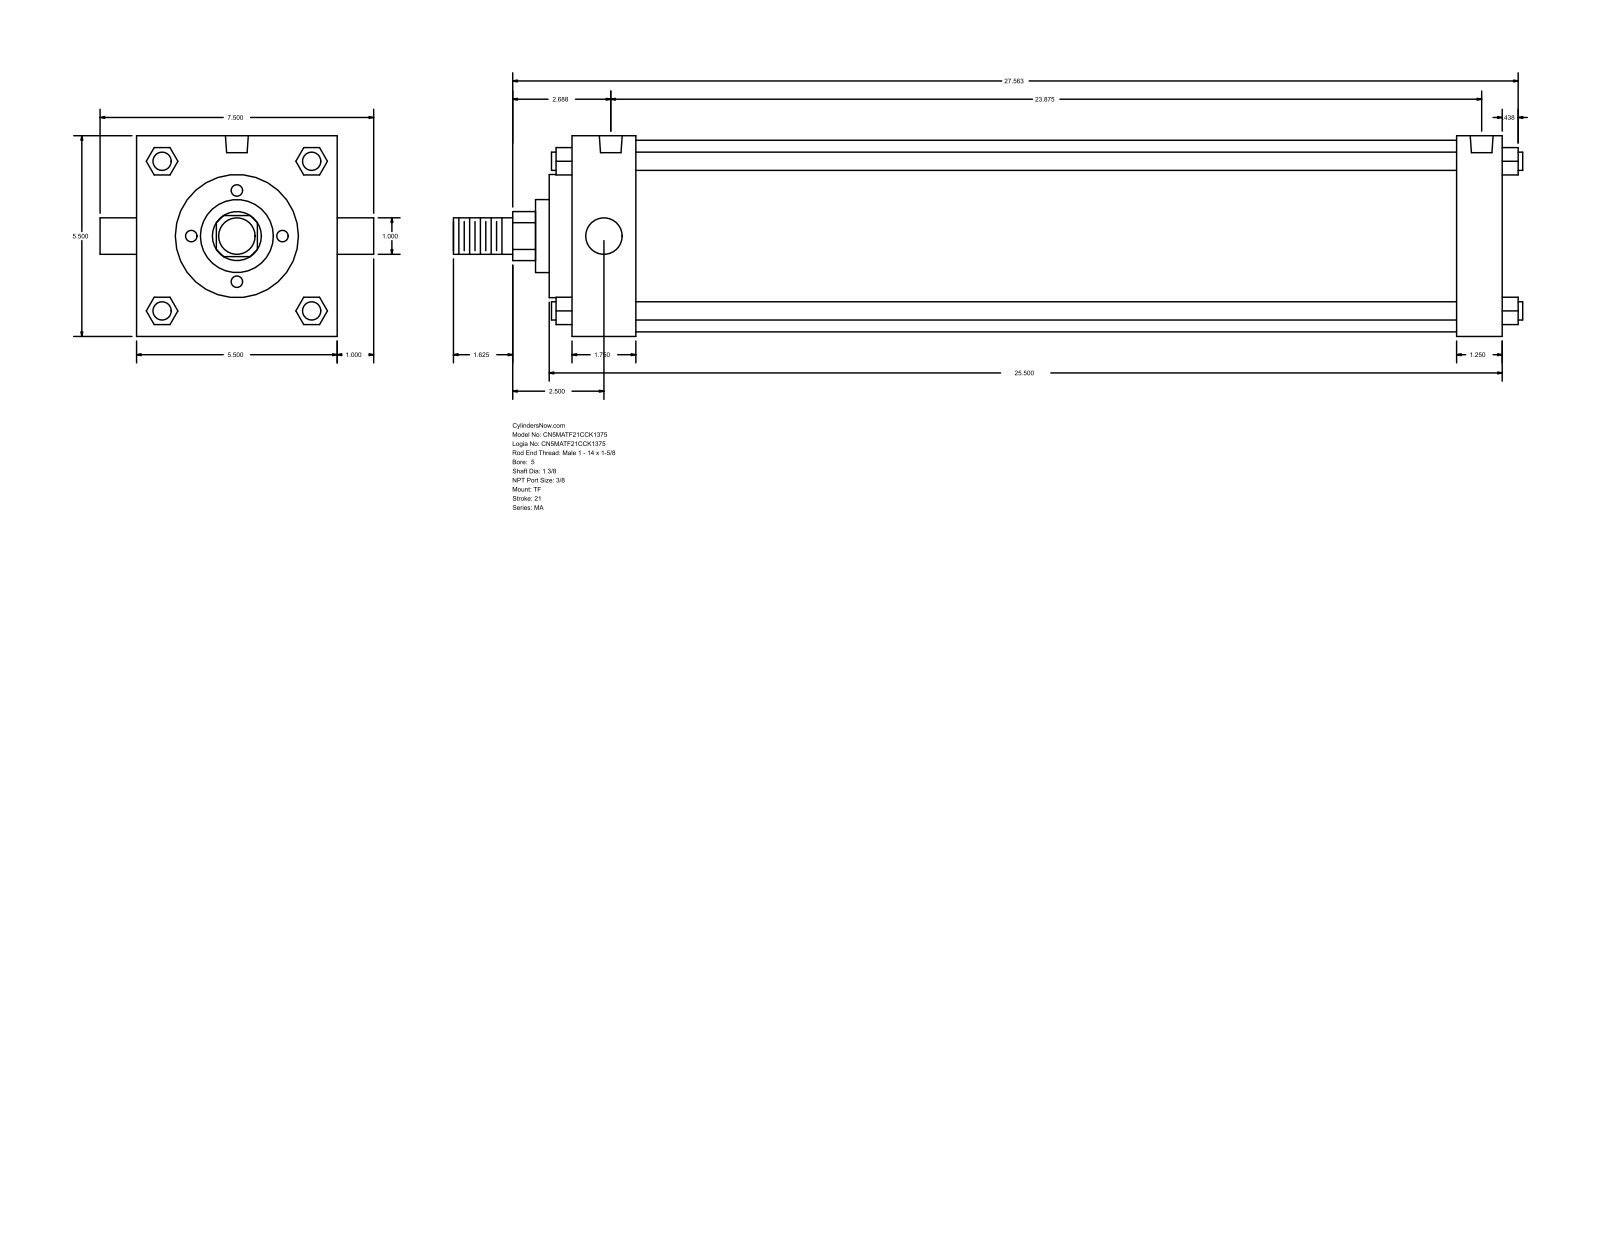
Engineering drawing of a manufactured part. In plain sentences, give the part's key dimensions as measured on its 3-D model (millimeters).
The part is named "MA_TF__0500_1.375". Its 3-D file was written by "GSSL Pune (CONFIG_CONTROL_DESIGN)". It is 0 solids with 122 faces: 93 planar, 29 cylindrical and 0 other. Overall it measures 744.54 by 190.5 by 139.7 millimeters. Round holes: 3 of diameter 11.11, 2 of diameter 15.93. Round bosses or shafts: 4 of diameter 12.7, 2 of diameter 25.4, 1 of diameter 133.35, 1 of diameter 85.72, 1 of diameter 50.8, 1 of diameter 34.92. Partial cylindrical surfaces (rounded edges, fillets, slot ends): 1 of radius 17.06. The main face-to-face distances are 139.7, 647.71, 615.96, 31.75, 44.45, 571.51, 603.26, 15.87, 60.32, 631.83. The hole center spacings are 4.77, 601.66, 596.89, 606.43.
